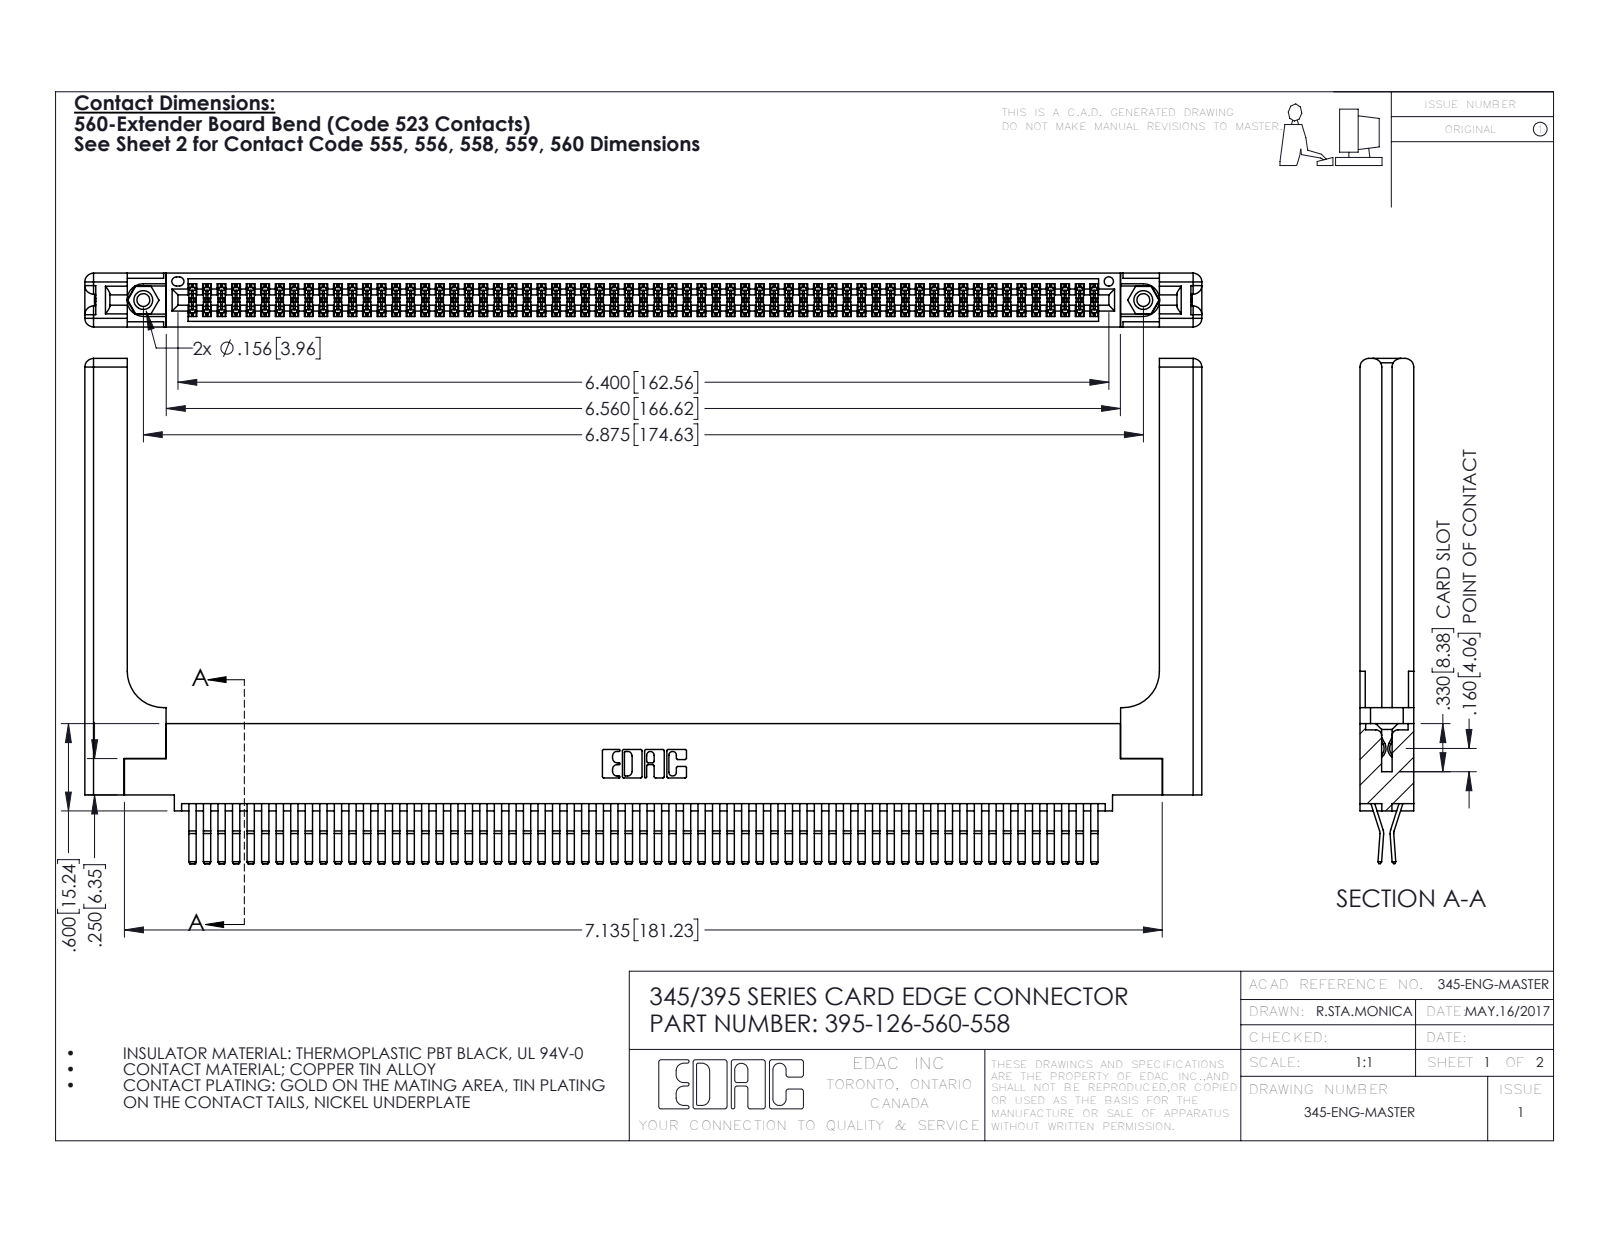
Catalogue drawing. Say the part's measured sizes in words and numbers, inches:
The part is named "395-126-560-558; 345-250-001_345-250-001-102; 345 Part_0.110 Offset - 0.156 Dia-TH; 345-220-058_345-220-058 (+1 more)". Its 3-D file was written by "SolidWorks 2016 (CONFIG_CONTROL_DESIGN)". It is 131 solids with 6938 faces: 4390 planar, 2488 cylindrical and 60 other. Overall it measures 7.679 by 3.472 by 0.37 inches. Its volume is 1.731 cubic inches and its surface area 57.49 square inches. Round holes: 2 of diameter 0.089, 2 of diameter 0.125, 2 of diameter 0.156, 1 of diameter 0.064. Round bosses or shafts: 2 of diameter 0.155. Partial cylindrical surfaces (rounded edges, fillets, slot ends): 190 of radius 0.006, 22 of radius 0.01, 16 of radius 0.06, 6 of radius 0.007, 6 of radius 0.031, 3 of radius 0.026, 2 of radius 0.01, 2 of radius 0.014. The main face-to-face distances are 0.072, 0.298, 0.025, 0.37, 0.098, 0.272, 0.2, 0.225, 0.148, 0.15. The hole center spacings are 0.27, 6.639, 6.875.
